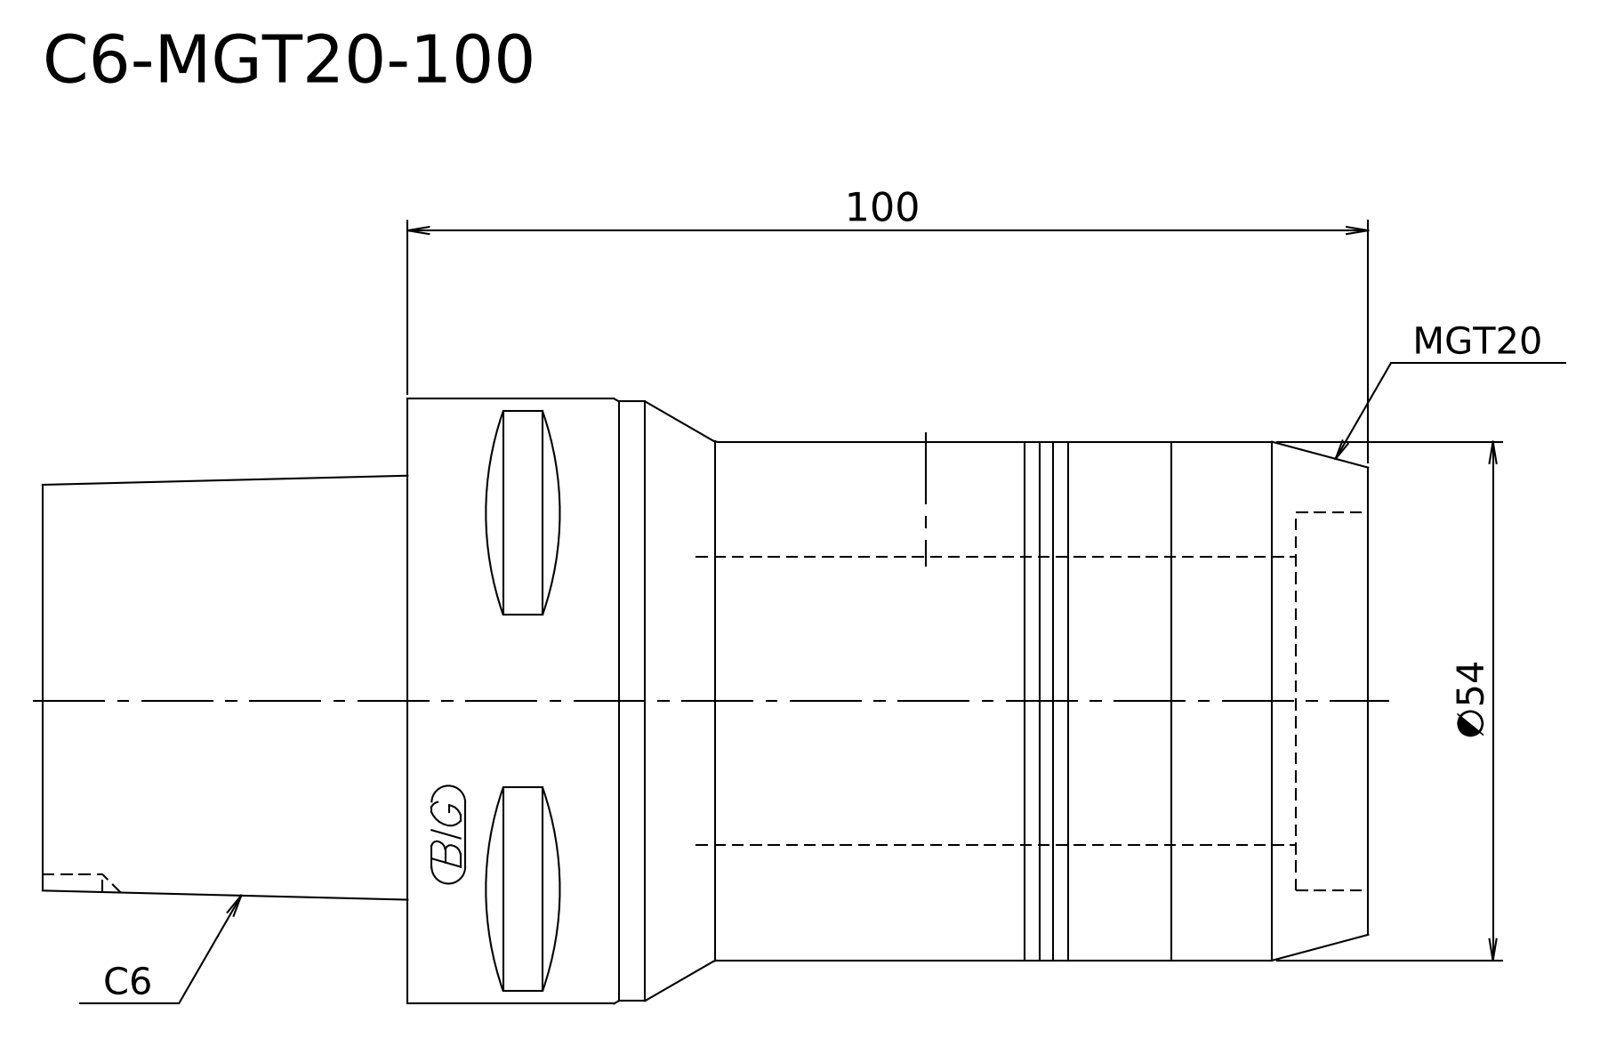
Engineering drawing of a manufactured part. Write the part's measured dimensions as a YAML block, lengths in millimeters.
step_written_by: "Kubotek KeyCreator V8.5.1 (14335) (CONFIG_CONTROL_DESIGN)"
units: millimeters
bodies: {solids: 1, faces: 10, planar: 3, cylindrical: 2, other: 5}
overall_size: [138, 62.98, 62.98]
volume: 304735
surface_area: 27955
round_bosses_or_shafts:
  - {diameter: 62.98, count: 1}
  - {diameter: 54, count: 1}
face_to_face_distances: [100, 138, 38]
